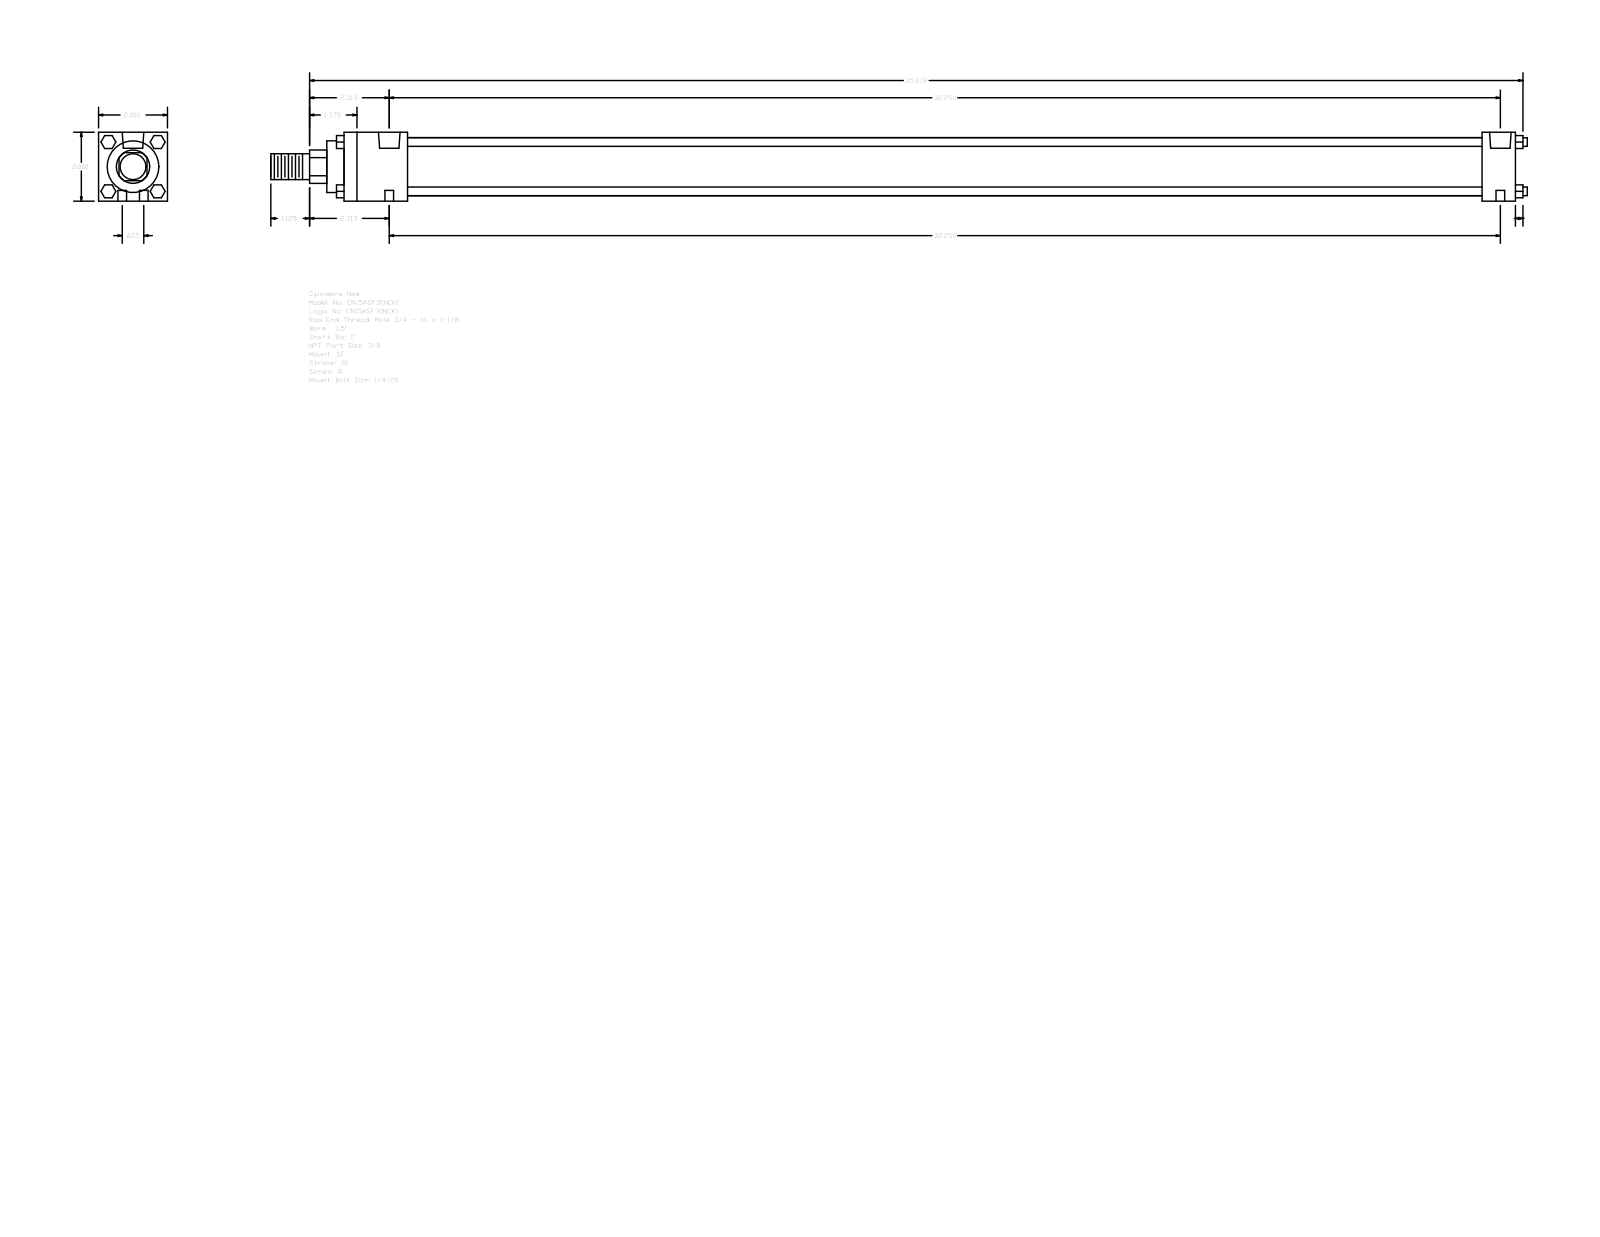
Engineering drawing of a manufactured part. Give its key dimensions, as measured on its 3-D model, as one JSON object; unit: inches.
{"part_name": "A_SF__0150_1", "step_written_by": "GSSL Pune (CONFIG_CONTROL_DESIGN)", "units": "inches", "bodies": {"solids": 0, "faces": 124, "planar": 94, "cylindrical": 30, "other": 0}, "overall_size": [36.469, 2, 2], "round_holes": [[0.25, 4], [0.219, 2], [0.627, 2]], "round_bosses_or_shafts": [[0.25, 4], [1.69, 1], [1.5, 1], [1, 1], [0.75, 1]], "partial_cylinders_radius": [[0.484, 1]], "face_to_face_distances": [2, 34, 1.844, 33.031, 31.187, 32.156, 0.969, 0.5, 2.344, 33.531], "hole_center_spacings": [0.313, 32.252, 32.25, 0.625, 32.256, 31.937]}
